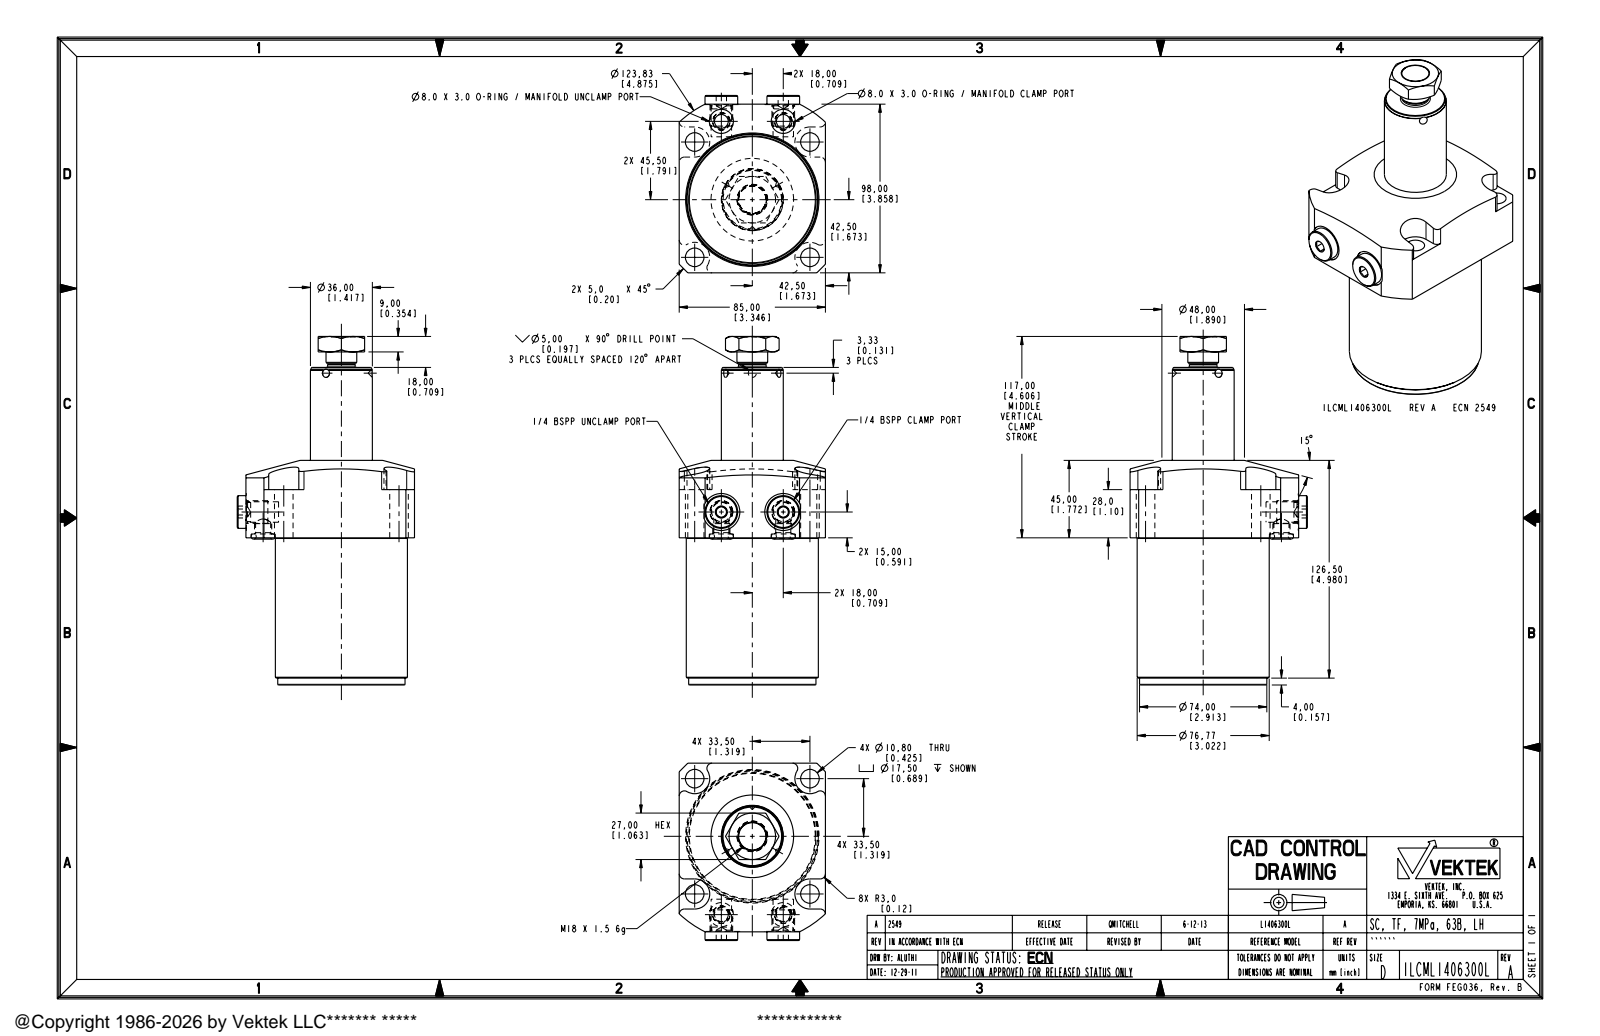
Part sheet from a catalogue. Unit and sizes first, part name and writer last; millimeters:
Units: millimetres
Overall size (bounding box): 202.5 × 103.05 × 85
Round holes (diameter × count): ⌀10.8 ×4, ⌀6 ×2, ⌀8.75 ×2, ⌀11.89 ×2, ⌀14 ×2, ⌀21.5 ×2, ⌀16.5 ×1
Round bosses / shafts (diameter × count): ⌀19 ×2, ⌀13.16 ×2, ⌀11.2 ×2, ⌀10 ×2, ⌀76.77 ×1, ⌀74 ×1, ⌀36 ×1, ⌀17.87 ×1
Partial cylindrical surfaces — rounded edges, fillets, slot ends (radius × count): R3 ×8, R8.75 ×4, R61.91 ×1
Main face-to-face distances: 85, 85.5, 98, 28, 130.5, 45, 113.5, 17, 18, 184.5
Hole centre spacings: 47.38, 67, 19.6, 36, 48.93, 52.88, 80.51, 94.3
Volume: 772 493 mm³ · Surface area: 67 494 mm²
Bodies: 3 solids, 205 faces (68 planar, 68 cylindrical, 69 other)
Part name (STEP PRODUCT): ILCML1406300L
STEP written by: PRO/ENGINEER BY PARAMETRIC TECHNOLOGY CORPORATION, 2007460 (AUTOMOTIVE_DESIGN_CC2)
